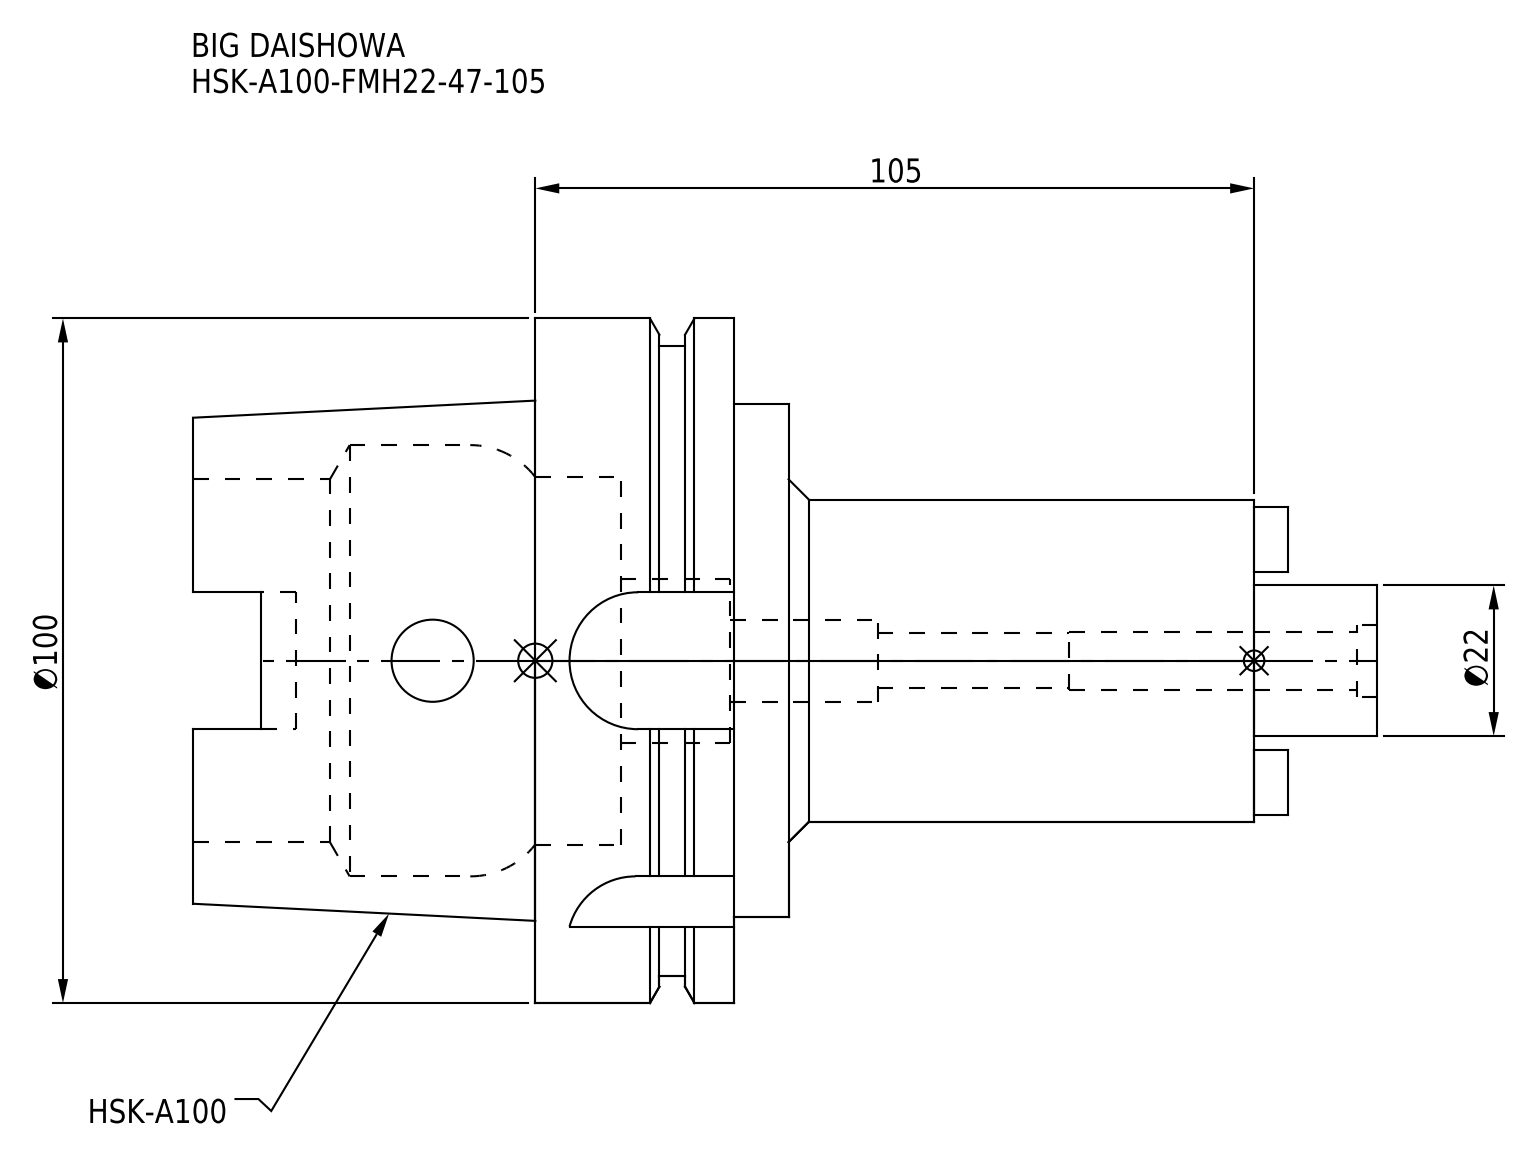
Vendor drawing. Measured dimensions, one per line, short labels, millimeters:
name: HSK-A100-FMH22-47-105
written by: CREO PARAMETRIC BY PTC INC, 2016380 (AUTOMOTIVE_DESIGN)
unit: mm
bodies: 1 solid, 109 faces (47 planar, 46 cylindrical, 16 other)
size: 173 × 100 × 100
volume: 408 812 mm³; area: 65 942 mm²
holes: 2× ⌀12, 1× ⌀8, 1× ⌀8.5, 1× ⌀10.5, 1× ⌀24, 1× ⌀53, 1× ⌀53.8, 1× ⌀63
bosses: 1× ⌀100, 1× ⌀92, 1× ⌀75, 1× ⌀47, 1× ⌀22
rounds: 4× R4.88, 4× R10
face distances: 29, 8, 37, 24.55, 16.55, 12.45, 105, 68, 76, 92.55
